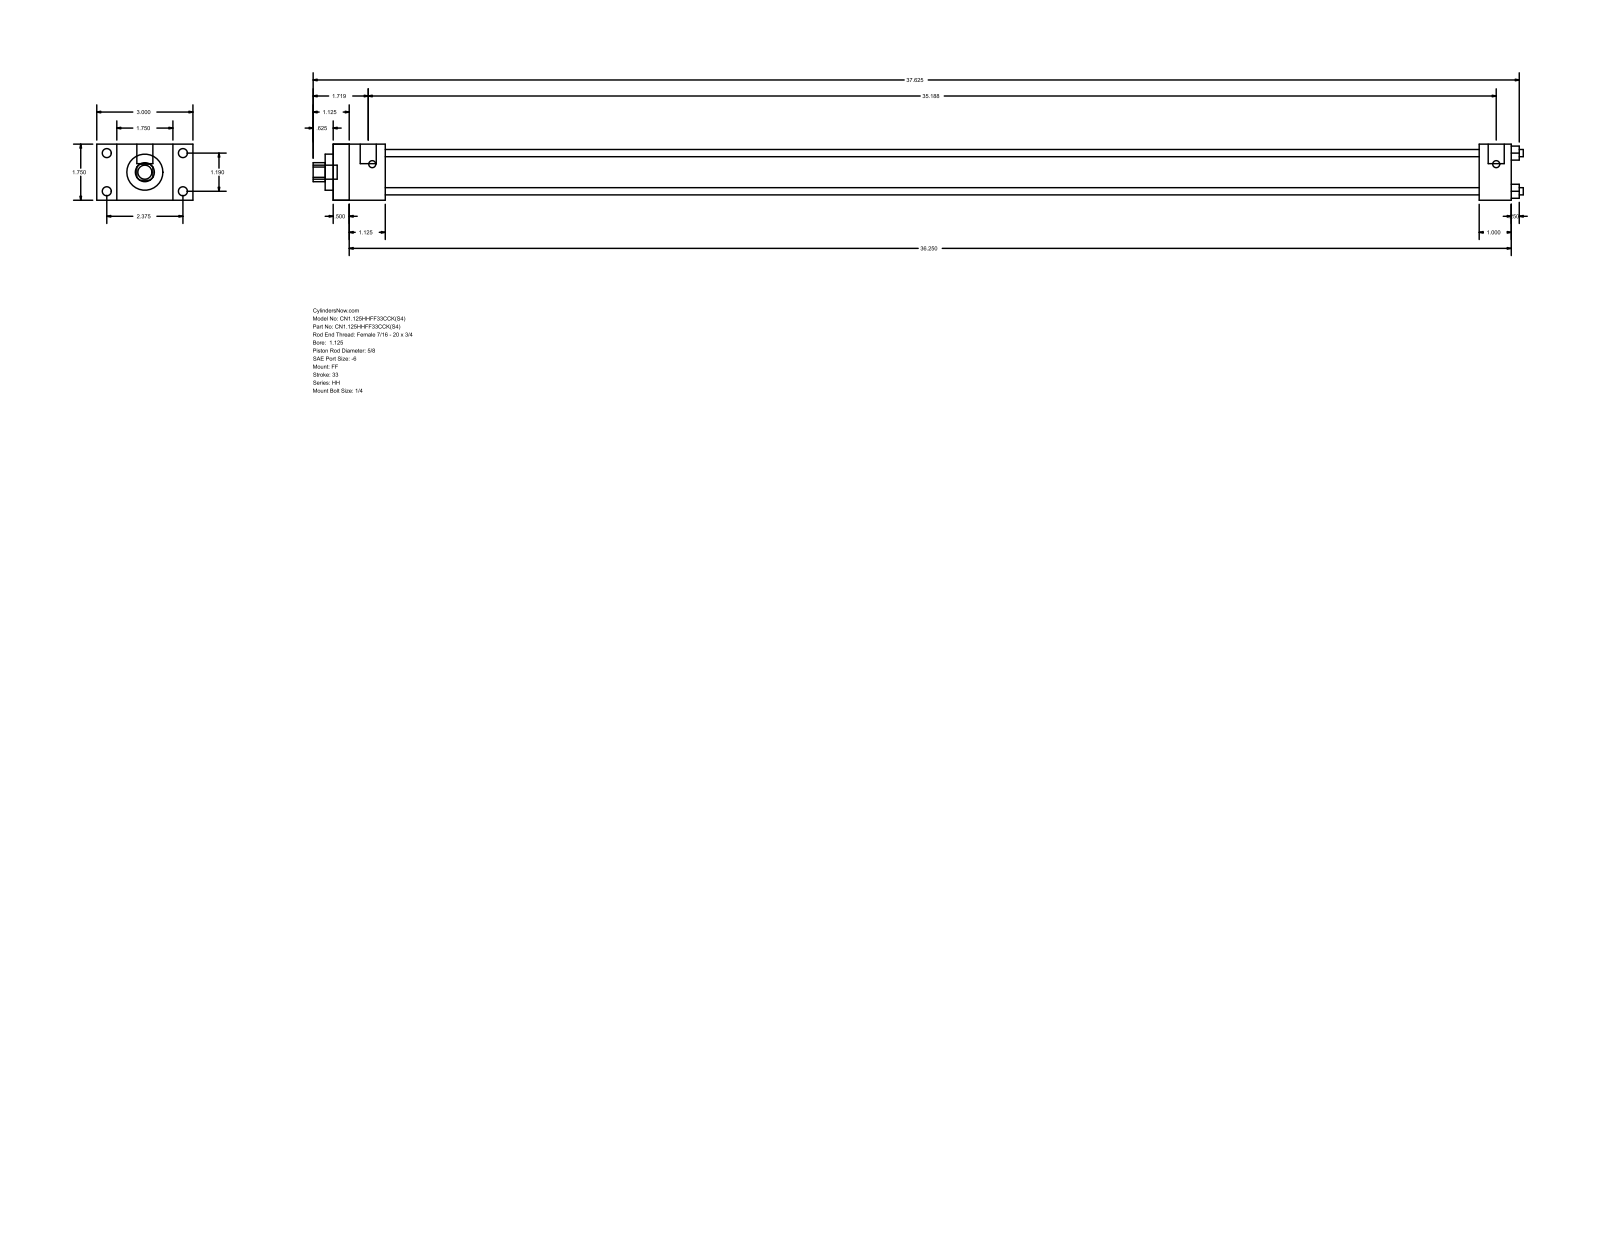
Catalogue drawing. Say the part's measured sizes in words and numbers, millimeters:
The part is named "HH_FF__0112_0.625". Its 3-D file was written by "GSSL Pune (CONFIG_CONTROL_DESIGN)". It is 0 solids with 92 faces: 64 planar, 28 cylindrical and 0 other. Overall it measures 958.85 by 76.2 by 44.45 millimeters. Round holes: 4 of diameter 5.71, 1 of diameter 15.88, 1 of diameter 28.57, 1 of diameter 34.92. Round bosses or shafts: 4 of diameter 7.14, 4 of diameter 5.56, 2 of diameter 12.7, 1 of diameter 11.11. Partial cylindrical surfaces (rounded edges, fillets, slot ends): 1 of radius 7.54. The main face-to-face distances are 44.46, 933.45, 12.69, 920.76, 15.87, 60.33, 28.58, 41.27, 908.04, 895.35. The hole center spacings are 21.37, 30.22, 42.74.
